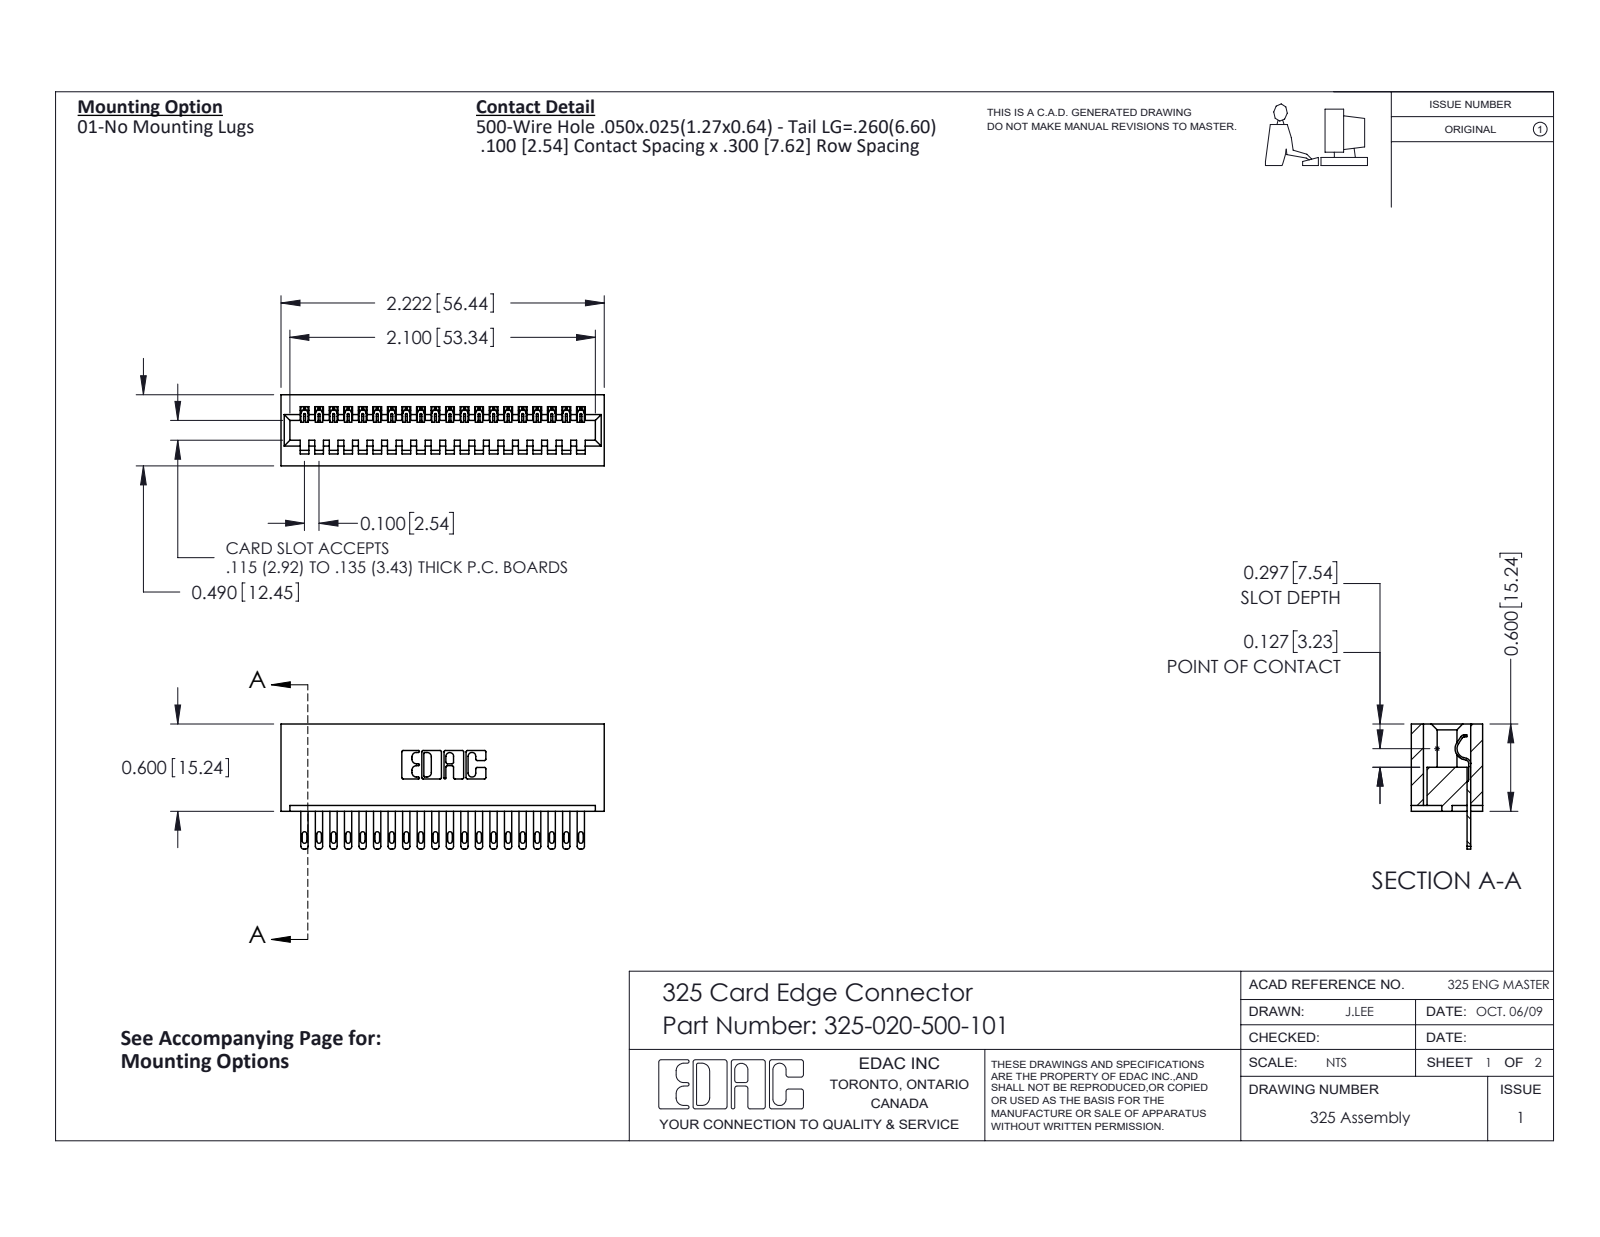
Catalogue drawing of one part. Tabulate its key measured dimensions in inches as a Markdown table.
| quantity | value |
| --- | --- |
| part name | 325-292-001_325-293-100; 325 Part_Lugless; 325-020-500-101 |
| STEP written by | SolidWorks 2016 (CONFIG_CONTROL_DESIGN) |
| units | inches |
| bodies | 21 solids, 1186 faces (786 planar, 400 cylindrical, 0 other) |
| overall size | 2.222 × 0.86 × 0.49 |
| volume | 0.462 in³ |
| surface area | 13.08 in² |
| partial cylindrical surfaces (radius × count) | 0.006 × 40, 0.016 × 40, 0.02 × 40, 0.01 × 22, 0.007 × 6, 0.031 × 6, 0.026 × 3, 0.014 × 1 |
| main face-to-face distances | 0.083, 0.407, 0.3, 0.49, 0.107, 0.383, 0.025, 0.1, 0.56, 0.4 |
